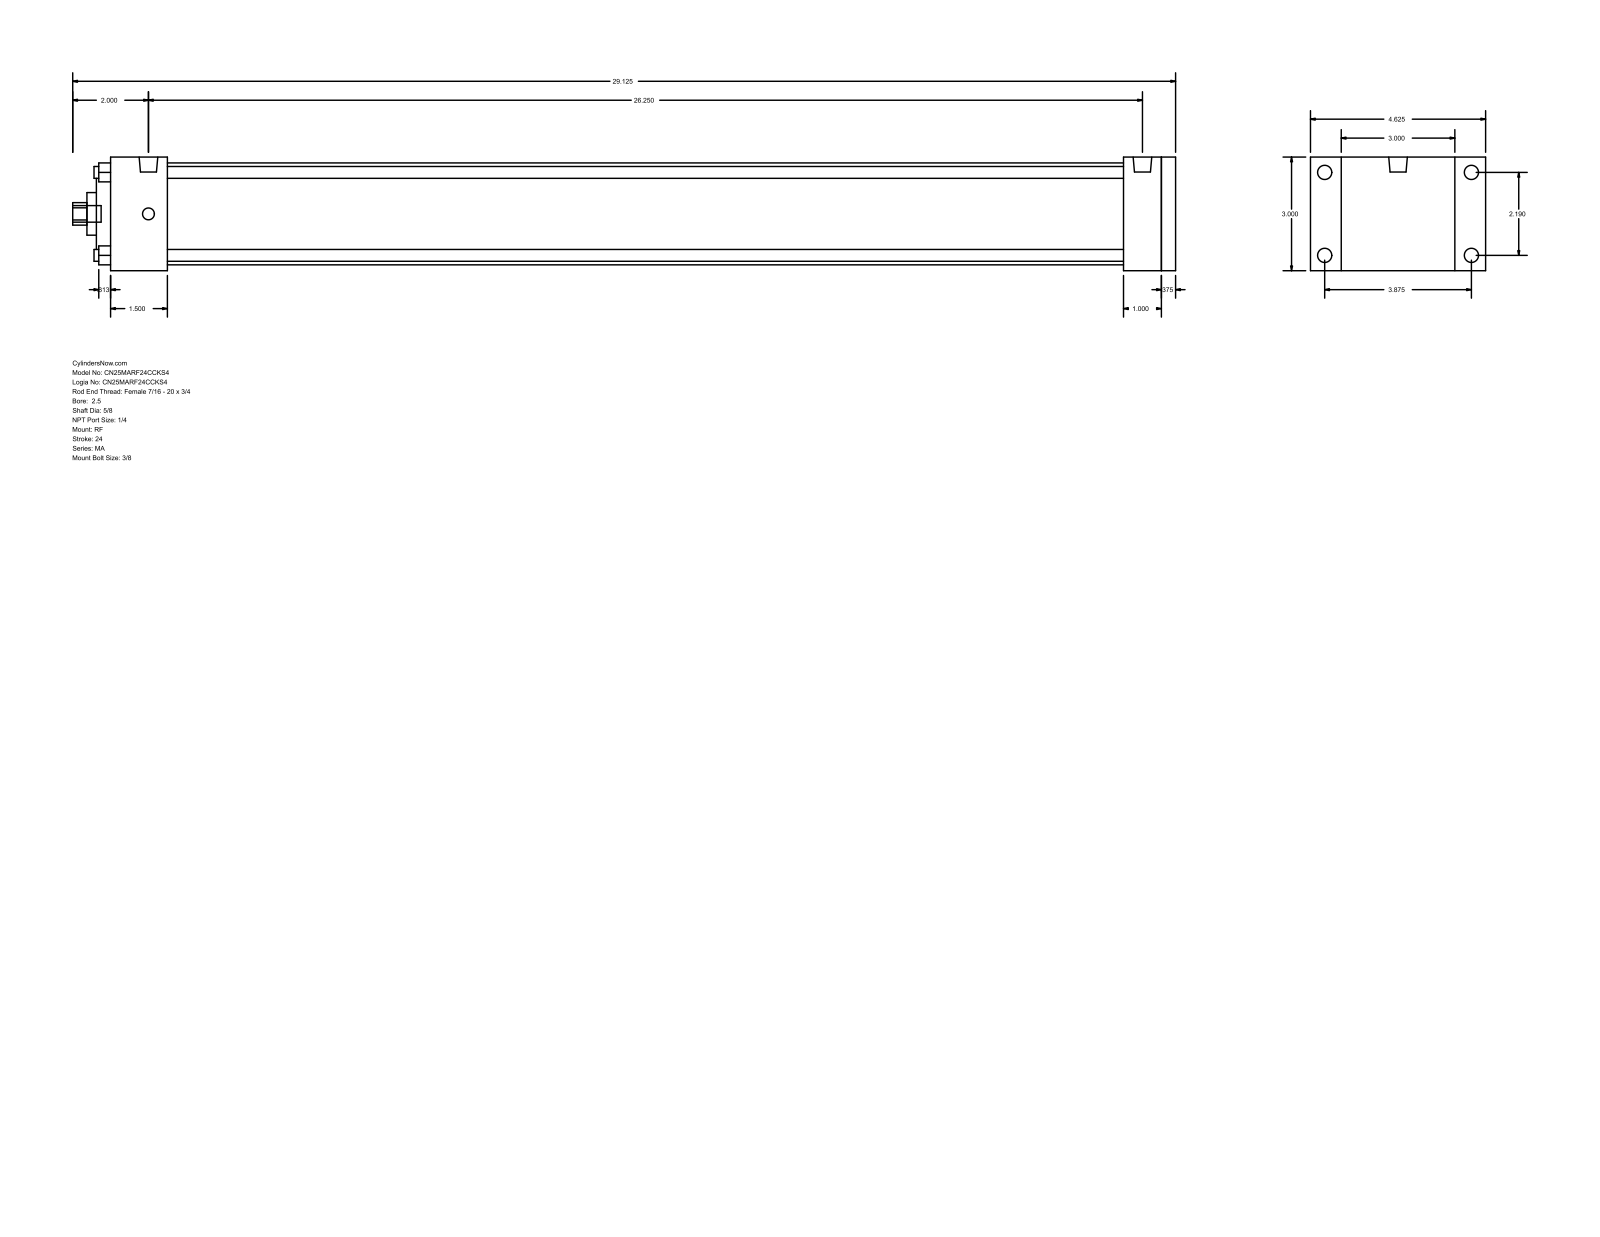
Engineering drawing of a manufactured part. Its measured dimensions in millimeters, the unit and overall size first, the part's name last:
Units: millimetres
Overall size (bounding box): 739.77 × 117.47 × 76.2
Round holes (diameter × count): ⌀7.94 ×4, ⌀15.88 ×1, ⌀28.57 ×1, ⌀50.8 ×1, ⌀68.33 ×1
Round bosses / shafts (diameter × count): ⌀9.53 ×4, ⌀7.94 ×4, ⌀12.49 ×2, ⌀11.11 ×1
Partial cylindrical surfaces — rounded edges, fillets, slot ends (radius × count): R7.54 ×1
Main face-to-face distances: 76.2, 714.37, 9.52, 704.85, 25.4, 38.1, 679.45, 641.35, 666.75, 676.27
Hole centre spacings: 39.33, 55.62, 78.66
Bodies: 0 solids, 94 faces (65 planar, 29 cylindrical, 0 other)
Part name (STEP PRODUCT): MA_RF__0250_0.625
STEP written by: GSSL Pune (CONFIG_CONTROL_DESIGN)
